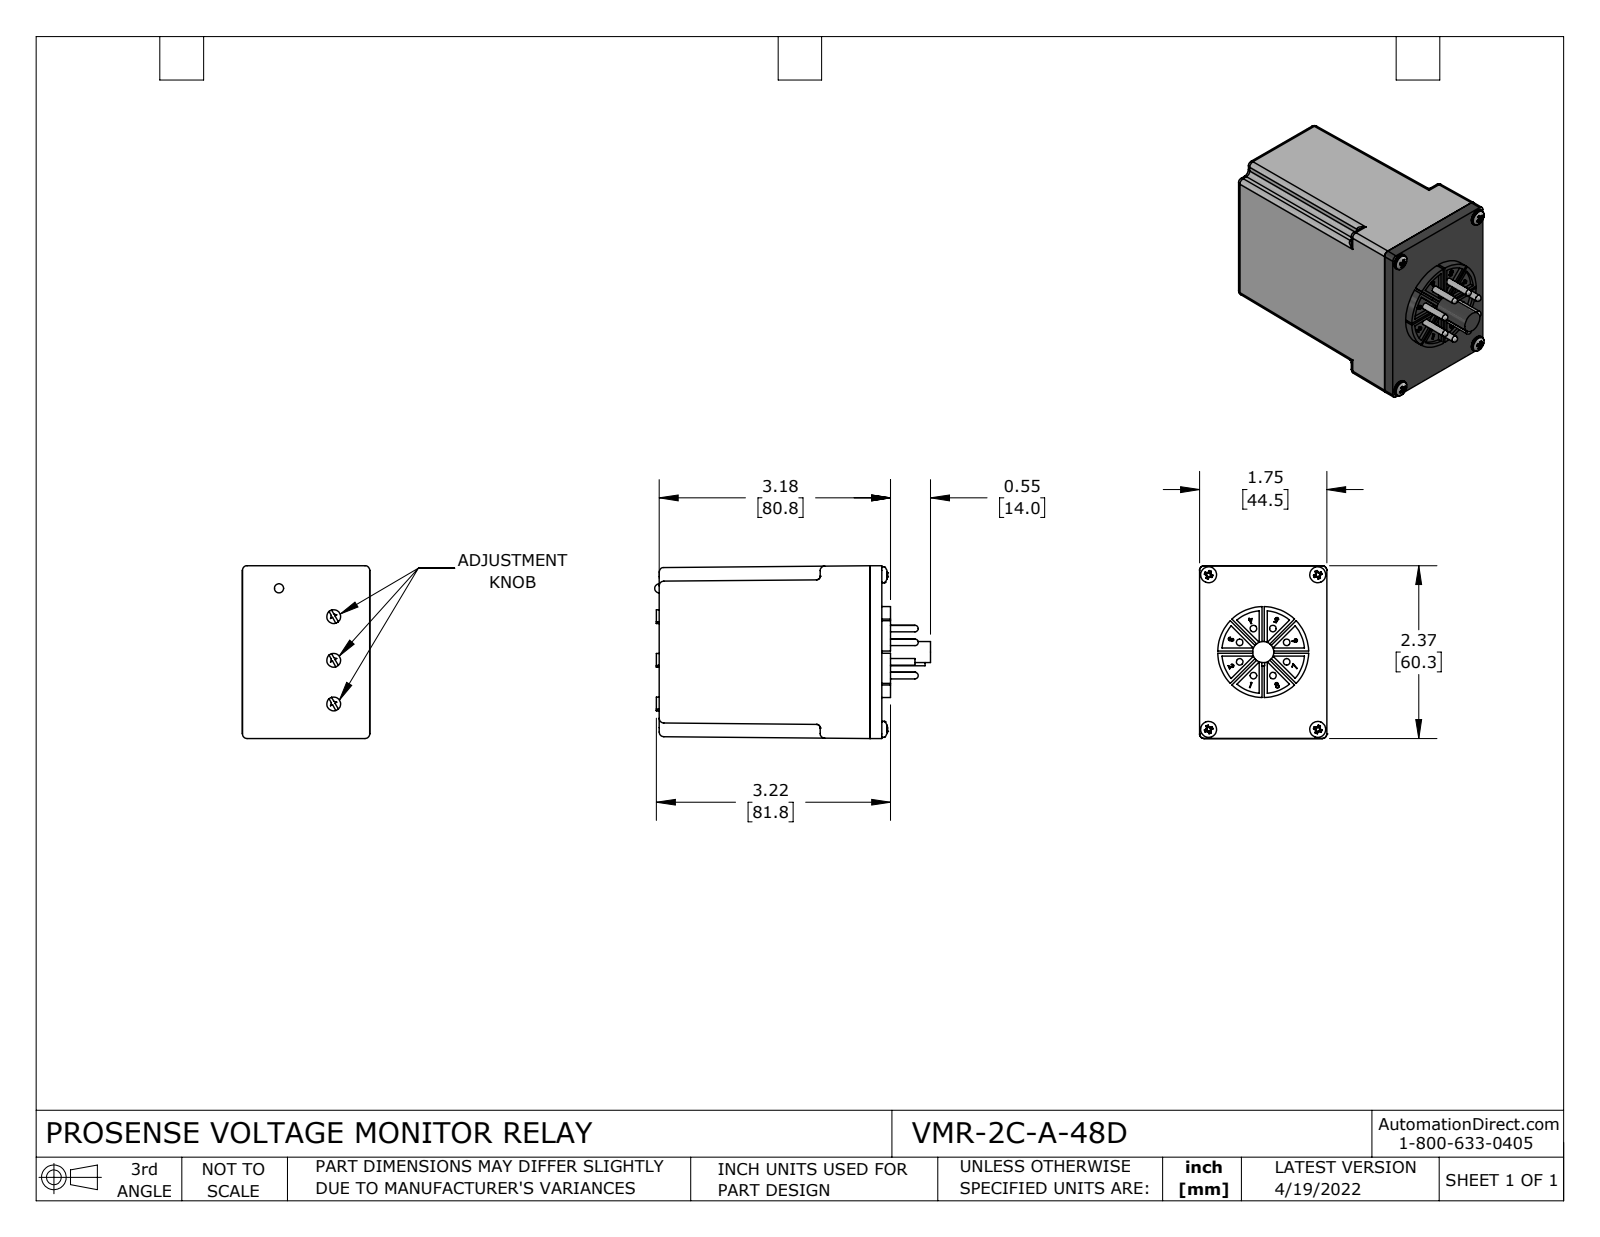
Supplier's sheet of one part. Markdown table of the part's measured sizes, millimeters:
| quantity | value |
| --- | --- |
| part name | VMR-2C-A-48D |
| STEP written by | SolidWorks 2021 (CONFIG_CONTROL_DESIGN) |
| units | millimeters |
| bodies | 18 solids, 574 faces (249 planar, 170 cylindrical, 155 other) |
| overall size | 96.3 × 60.3 × 44.5 |
| volume | 200 700 mm³ |
| surface area | 28 850 mm² |
| round holes (diameter × count) | 3.2 × 4 |
| round bosses / shafts (diameter × count) | 2.3 × 8, 5.6 × 4, 4.8 × 3, 31.8 × 1, 7.4 × 1 |
| partial cylindrical surfaces (radius × count) | 1.6 × 32, 0.1 × 8, 1.3 × 4, 14.5 × 1 |
| main face-to-face distances | 73.7, 4.1, 77.7, 1.8, 5.8, 79.5, 4.8, 1.3, 3, 7.1 |
| hole center spacings | 38.1, 54, 66.1 |
